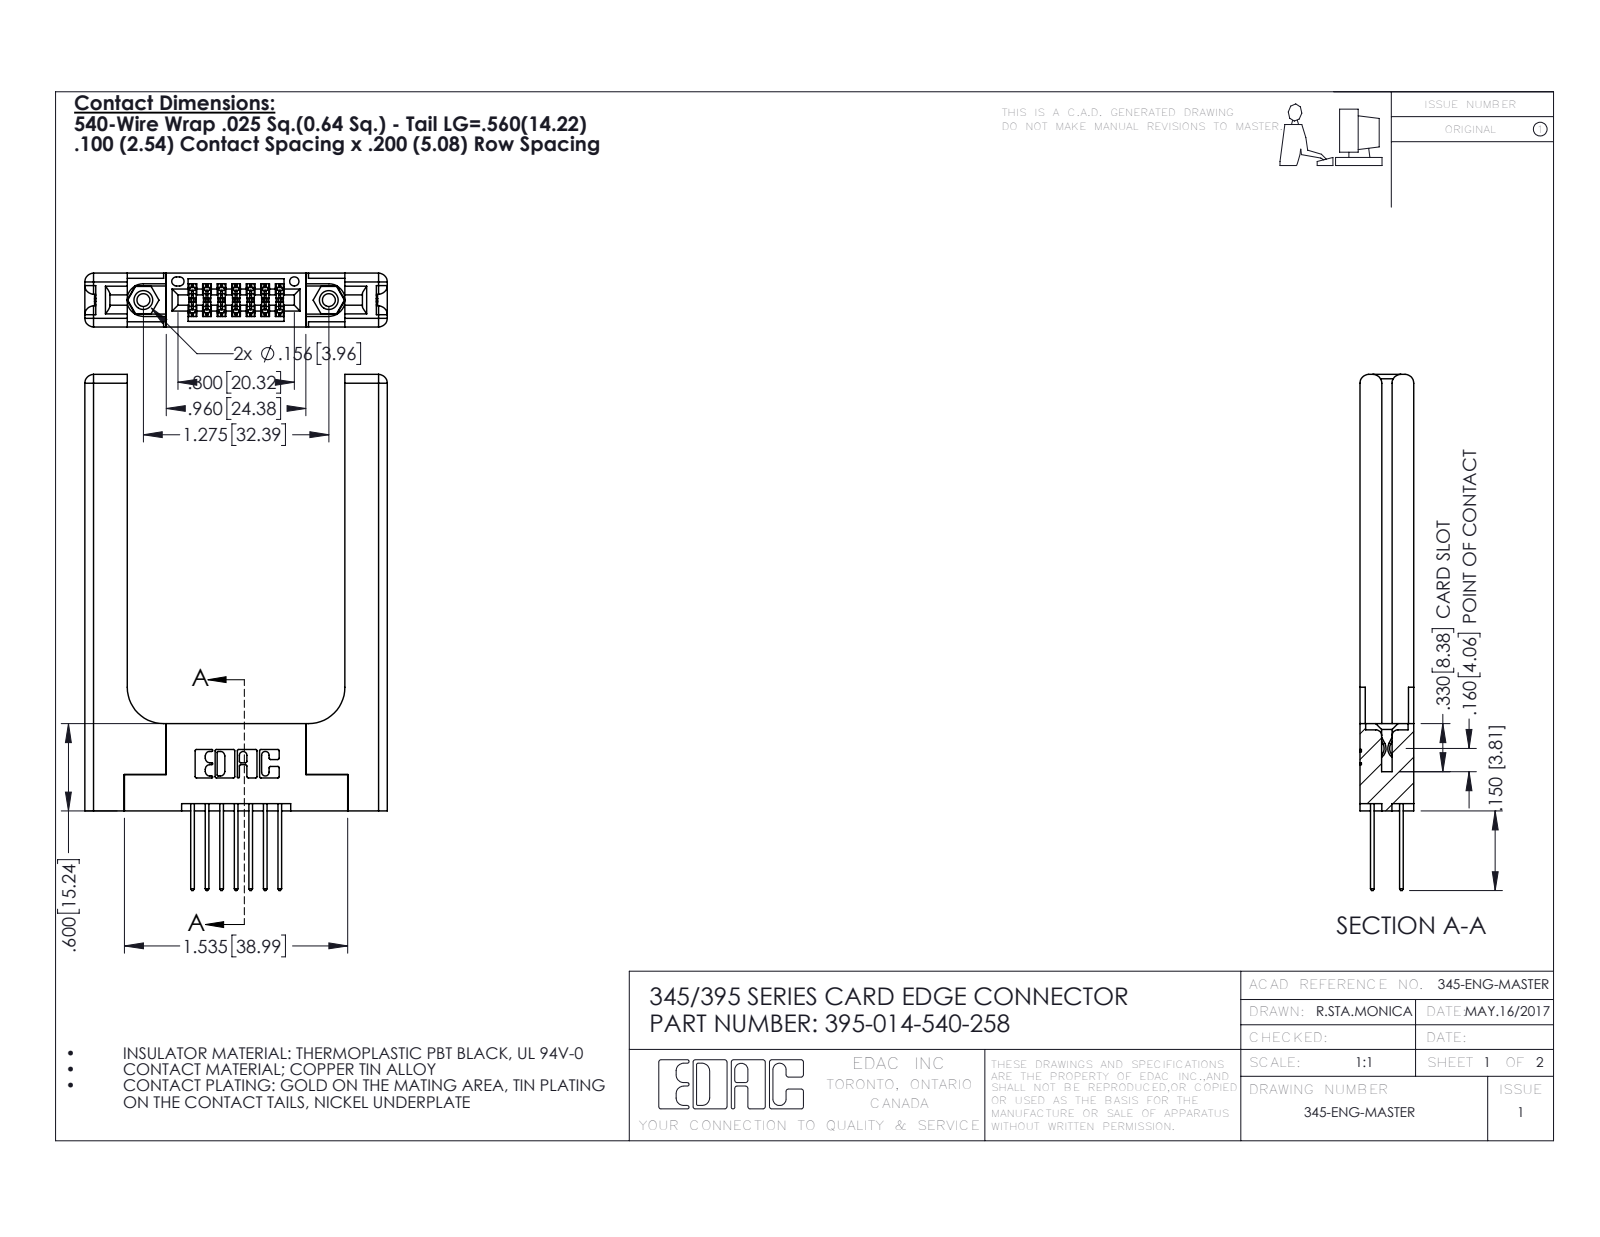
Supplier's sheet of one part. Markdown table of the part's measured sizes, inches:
| quantity | value |
| --- | --- |
| part name | 395-014-540-258; 345-250-001_345-250-001-102; 345 Part_Flush Mounting Lugs - 0.156 Dia-TH; 345-292-001_345-293-140 (+1 more) |
| STEP written by | SolidWorks 2016 (CONFIG_CONTROL_DESIGN) |
| units | inches |
| bodies | 19 solids, 1082 faces (690 planar, 332 cylindrical, 60 other) |
| overall size | 3.547 × 2.079 × 0.37 |
| volume | 0.814 in³ |
| surface area | 18.3 in² |
| round holes (diameter × count) | 0.089 × 2, 0.125 × 2, 0.156 × 2, 0.064 × 1 |
| round bosses / shafts (diameter × count) | 0.155 × 2 |
| partial cylindrical surfaces (radius × count) | 0.01 × 22, 0.006 × 21, 0.06 × 16, 0.01 × 14, 0.007 × 6, 0.031 × 6, 0.026 × 3, 0.014 × 2 |
| main face-to-face distances | 0.37, 0.15, 0.072, 0.22, 0.077, 0.148, 0.298, 0.2, 1.496, 0.225 |
| hole center spacings | 0.27, 1.045, 1.275 |
